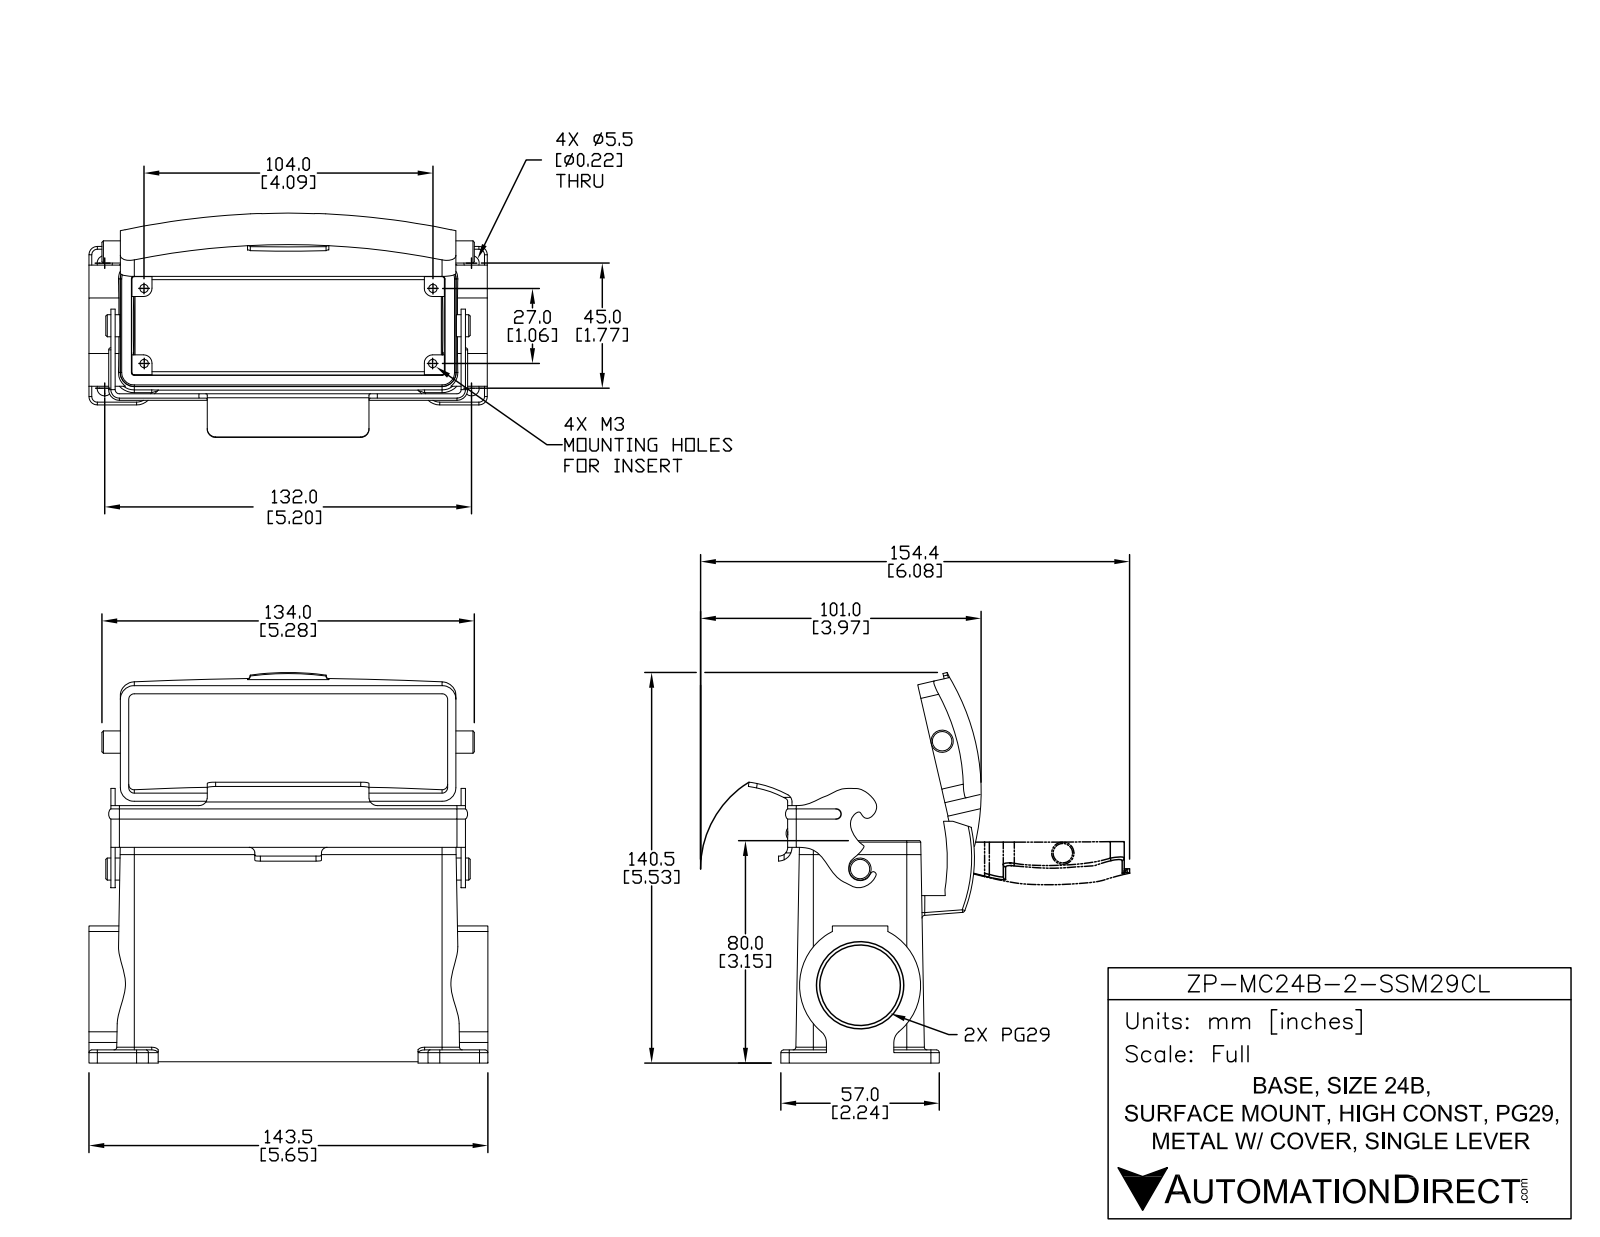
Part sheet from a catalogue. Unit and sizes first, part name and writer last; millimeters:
Units: millimetres
Overall size (bounding box): 143.5 × 140.5 × 80.75
Round holes (diameter × count): ⌀3 ×4, ⌀5.5 ×4, ⌀2 ×1, ⌀25.23 ×1, ⌀30 ×1, ⌀35.5 ×1
Round bosses / shafts (diameter × count): ⌀8 ×1, ⌀7.95 ×1, ⌀6.8 ×1
Partial cylindrical surfaces — rounded edges, fillets, slot ends (radius × count): R1 ×26, R3 ×12, R2 ×8, R5 ×6, R0.5 ×4, R6 ×4, R1.5 ×2, R3.06 ×2
Main face-to-face distances: 39.67, 4, 4.5, 0.5, 1.56, 3, 116.8, 40.48, 7.95, 120.75
Hole centre spacings: 16.64, 38.63, 53.72, 69.73, 118.34, 123.37, 27, 45
Volume: 207 478 mm³ · Surface area: 99 718 mm²
Bodies: 3 solids, 469 faces (157 planar, 182 cylindrical, 130 other)
Part name (STEP PRODUCT): ZP-MC24B-2-SSM29CL
STEP written by: SolidWorks 2014 (AUTOMOTIVE_DESIGN)
